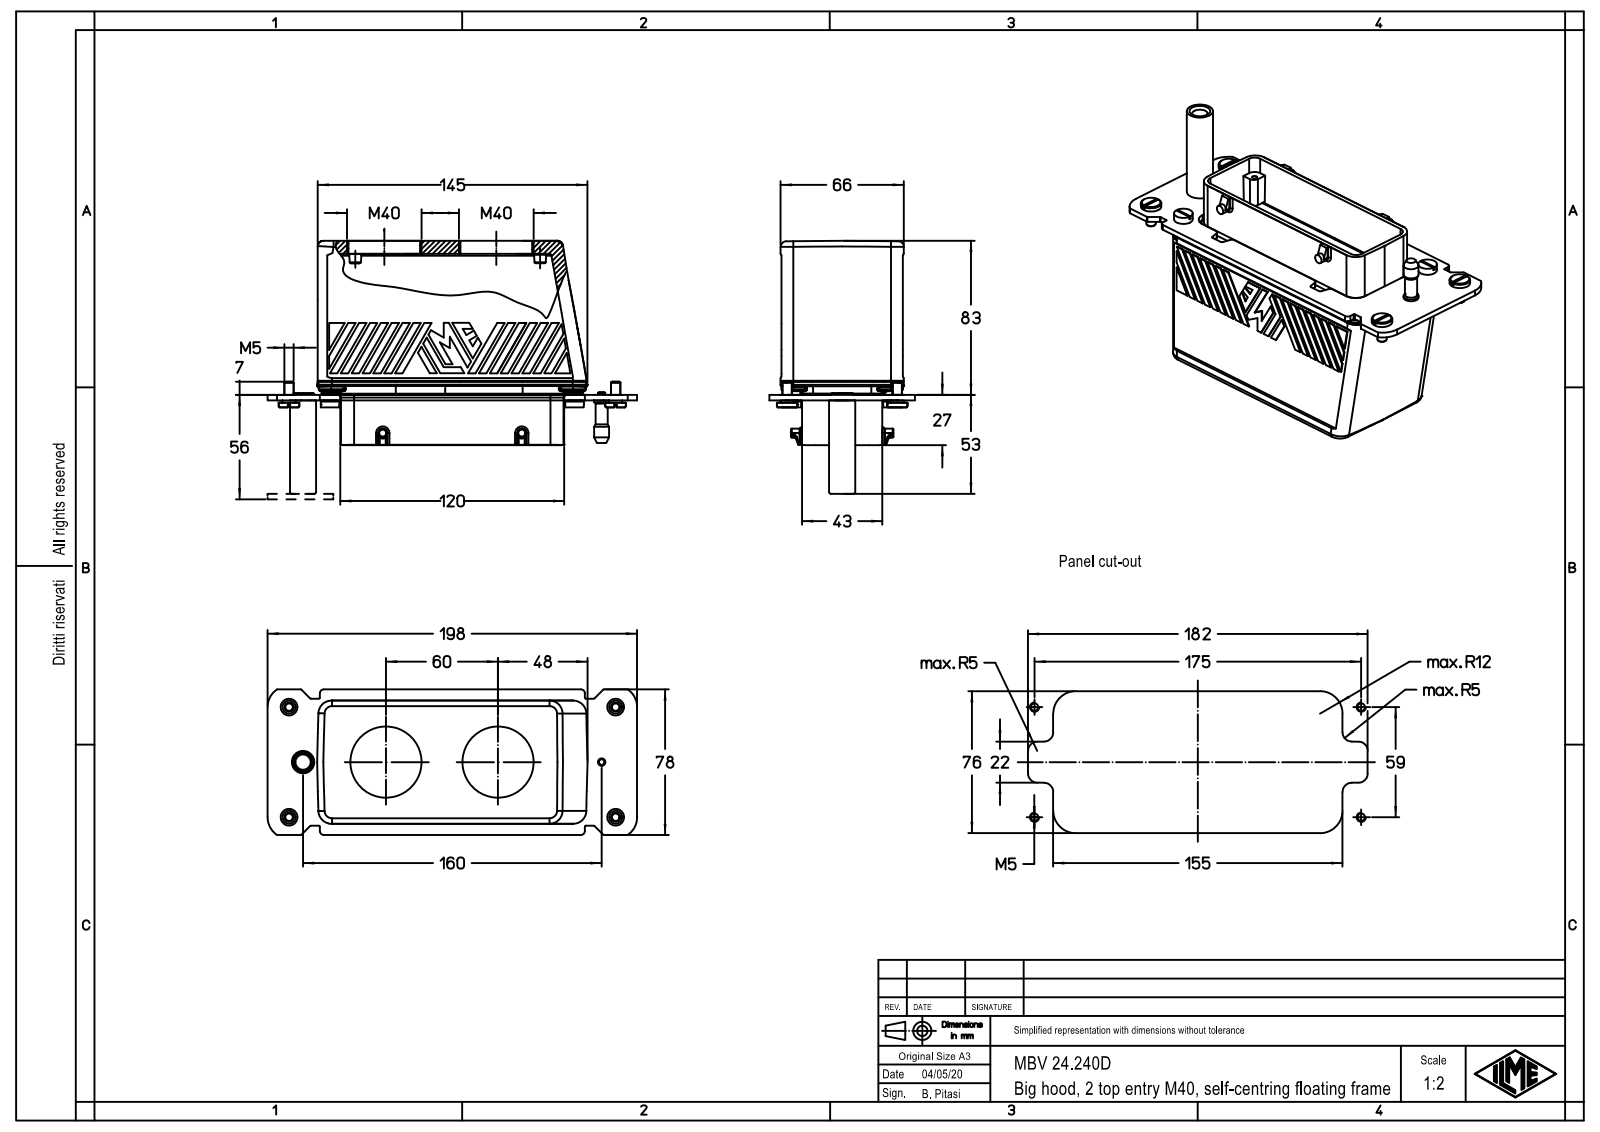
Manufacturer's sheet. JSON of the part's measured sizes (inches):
{"part_name": "MBV 24.240D", "step_written_by": "Creo Elements/Direct Modeling 20.1B 02-Apr-2019 (C) Parametric Technology GmbH (AUTOMOTIVE_DESIGN)", "units": "inches", "bodies": {"solids": 1, "faces": 927, "planar": 475, "cylindrical": 232, "other": 220}, "overall_size": [7.795, 5.323, 3.071], "volume_in3": 43.73, "surface_area_in2": 155.8, "round_holes": [[0.354, 4], [0.201, 2], [0.283, 2], [1.575, 2], [0.159, 1], [0.323, 1], [0.378, 1], [0.474, 1]], "round_bosses_or_shafts": [[0.197, 6], [0.433, 4], [0.276, 4], [0.394, 2], [0.366, 2], [0.189, 2], [0.551, 1], [0.472, 1]], "partial_cylinders_radius": [[0.039, 52], [0.02, 20], [0.276, 16], [0.079, 14], [0.012, 6], [0.059, 6], [0.118, 6], [0.165, 4]], "face_to_face_distances": [0.118, 2.559, 2.126, 3.355, 3.237, 0.433, 0.016, 0.449, 2.142, 2.575], "hole_center_spacings": [1.198, 6.696, 0.872, 1.207, 2.322, 2.323, 2.387, 2.772]}
